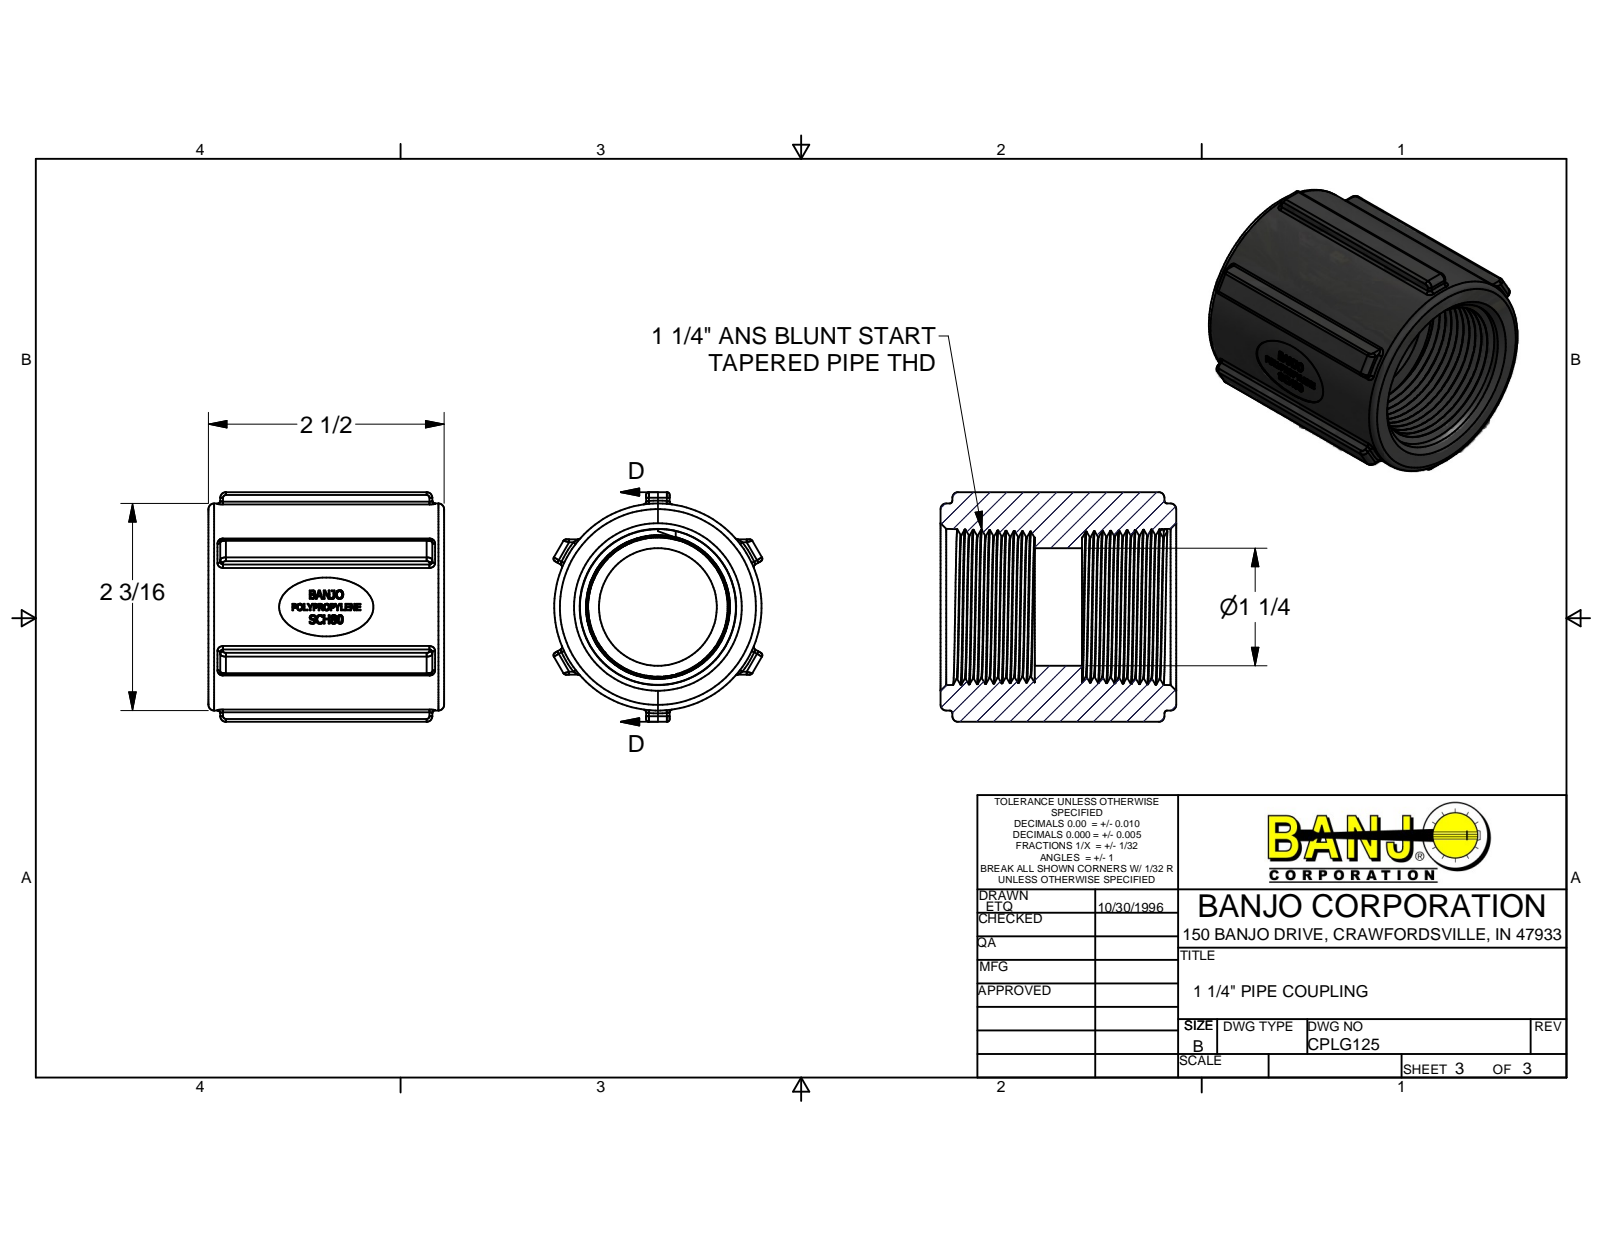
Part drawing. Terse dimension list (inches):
name: CPLG125
written by: Autodesk Inventor 2014 (AUTOMOTIVE_DESIGN)
unit: in
bodies: 1 solid, 546 faces (195 planar, 99 cylindrical, 252 other)
size: 2.5 × 2.44 × 2.216
volume: 5.389 in³; area: 43.05 in²
holes: 1× ⌀1.25
bosses: 1× ⌀2.2
rounds: 40× R0.03, 12× R0.06, 1× R1.09
face distances: 1, 1.5, 2.44, 2.5, 0.502, 1.938, 0.5, 1.436, 0.25, 0.25
